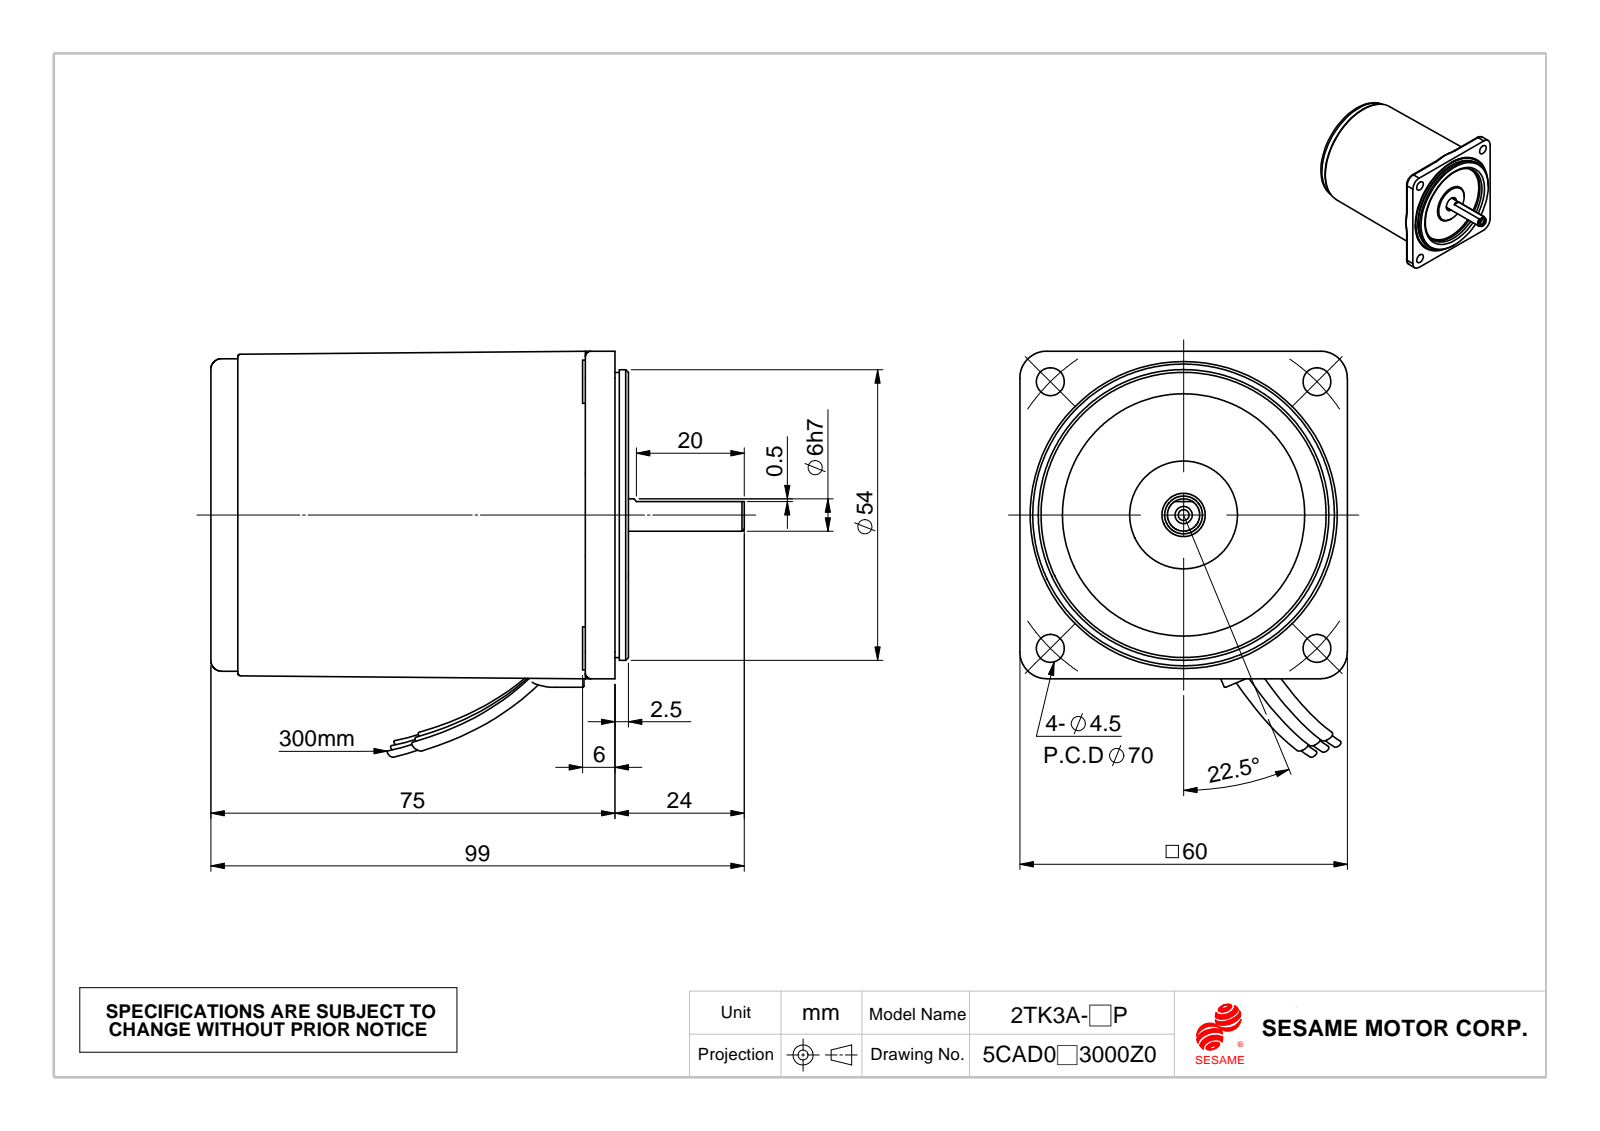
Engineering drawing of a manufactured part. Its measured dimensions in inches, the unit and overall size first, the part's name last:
Units: inches
Overall size (bounding box): 3.898 × 2.967 × 2.394
Round holes (diameter × count): ⌀0.205 ×4, ⌀0.079 ×1, ⌀0.098 ×1, ⌀0.276 ×1, ⌀0.283 ×1, ⌀0.374 ×1, ⌀1.268 ×1, ⌀1.772 ×1, ⌀2.205 ×1
Round bosses / shafts (diameter × count): ⌀0.315 ×4, ⌀2.283 ×1, ⌀2.123 ×1, ⌀2.084 ×1, ⌀0.366 ×1, ⌀0.237 ×1, ⌀0.236 ×1, ⌀0.225 ×1
Partial cylindrical surfaces — rounded edges, fillets, slot ends (radius × count): R0.01 ×8, R0.039 ×4, R0.197 ×4, R0.207 ×1, R1.143 ×1
Main face-to-face distances: 0.059, 0.063, 2.953, 2.89, 2.894, 0.02, 0.039, 2.933, 0.043, 0.031
Hole centre spacings: 1.378, 1.949, 2.756
Volume: 13.31 in³ · Surface area: 46.8 in²
Bodies: 7 solids, 221 faces (66 planar, 74 cylindrical, 81 other)
Part name (STEP PRODUCT): 06A_0成品; M206_Default; C254_Default; 線扣
STEP written by: SolidWorks 2010 (CONFIG_CONTROL_DESIGN)
